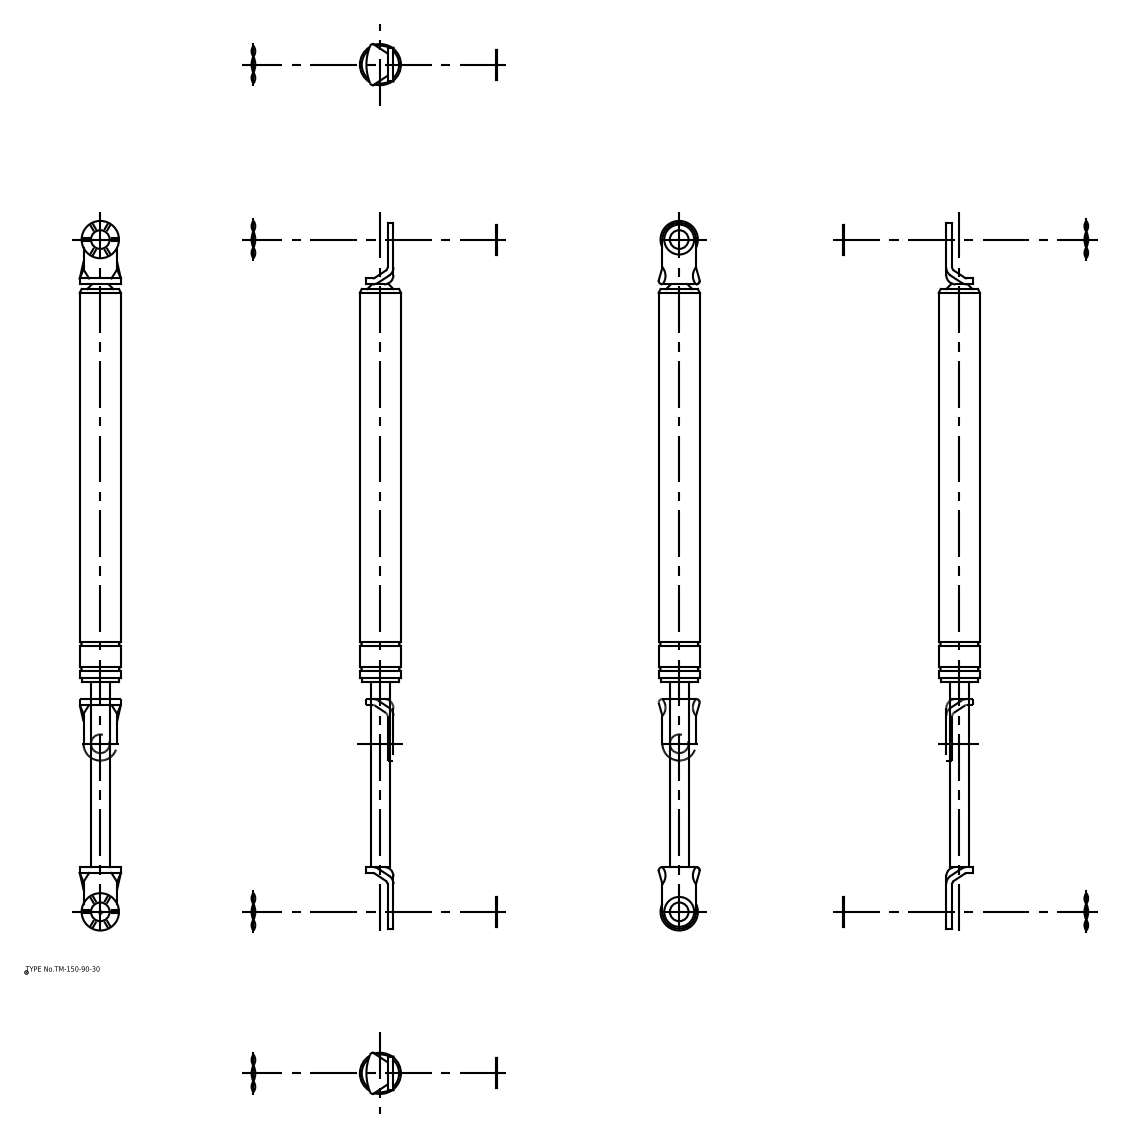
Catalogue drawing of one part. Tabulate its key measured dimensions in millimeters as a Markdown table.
| quantity | value |
| --- | --- |
| part name | ウェーブワッシャー; ワッシャー; 本体; 本体_div |
| STEP written by | spGate 16.7.1 (AUTOMOTIVE_DESIGN) |
| units | millimeters |
| bodies | 6 solids, 94 faces (42 planar, 44 cylindrical, 8 other) |
| overall size | 380 × 22.5 × 22.5 |
| volume | 93 574 mm³ |
| surface area | 24 158 mm² |
| round holes (diameter × count) | 10 × 2 |
| round bosses / shafts (diameter × count) | 20 × 3, 16 × 2, 22.5 × 1, 22 × 1, 10 × 1 |
| partial cylindrical surfaces (radius × count) | 4.4 × 2, 5 × 2, 9 × 2, 26.32 × 1 |
| main face-to-face distances | 3.2, 2, 5.2, 315.2, 5.7, 3.7, 0.5, 216.2, 102.2, 318.4 |
| hole center spacings | 360 |
